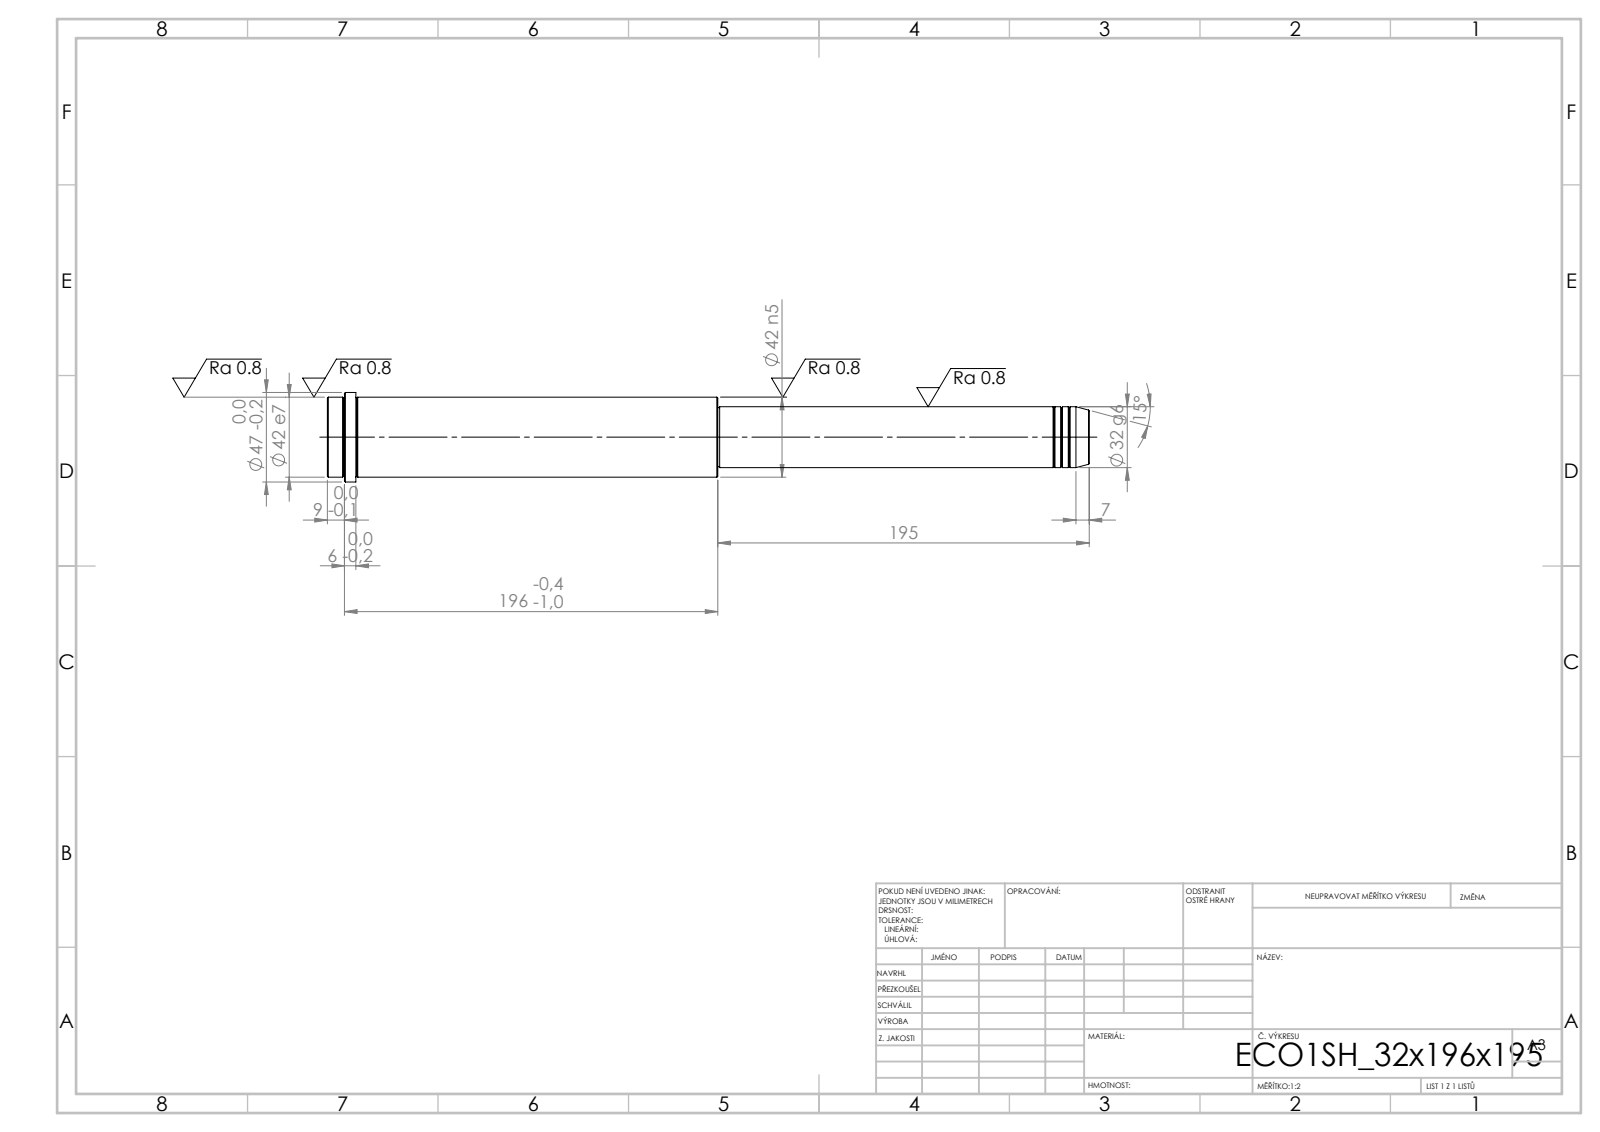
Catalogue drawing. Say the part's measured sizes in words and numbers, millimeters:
Its 3-D file was written by "SolidWorks 2019 (CONFIG_CONTROL_DESIGN)". It is 1 solid with 52 faces: 6 planar, 16 cylindrical and 30 other. Overall it measures 400 by 47 by 47 millimeters. Its volume is 441 984 cubic millimeters and its surface area 50 293 square millimeters. Round bosses or shafts: 1 of diameter 47, 1 of diameter 42, 1 of diameter 32, 1 of diameter 31. The main face-to-face distances are 400, 195, 205, 385, 190, 15, 391, 196, 6, 9.
